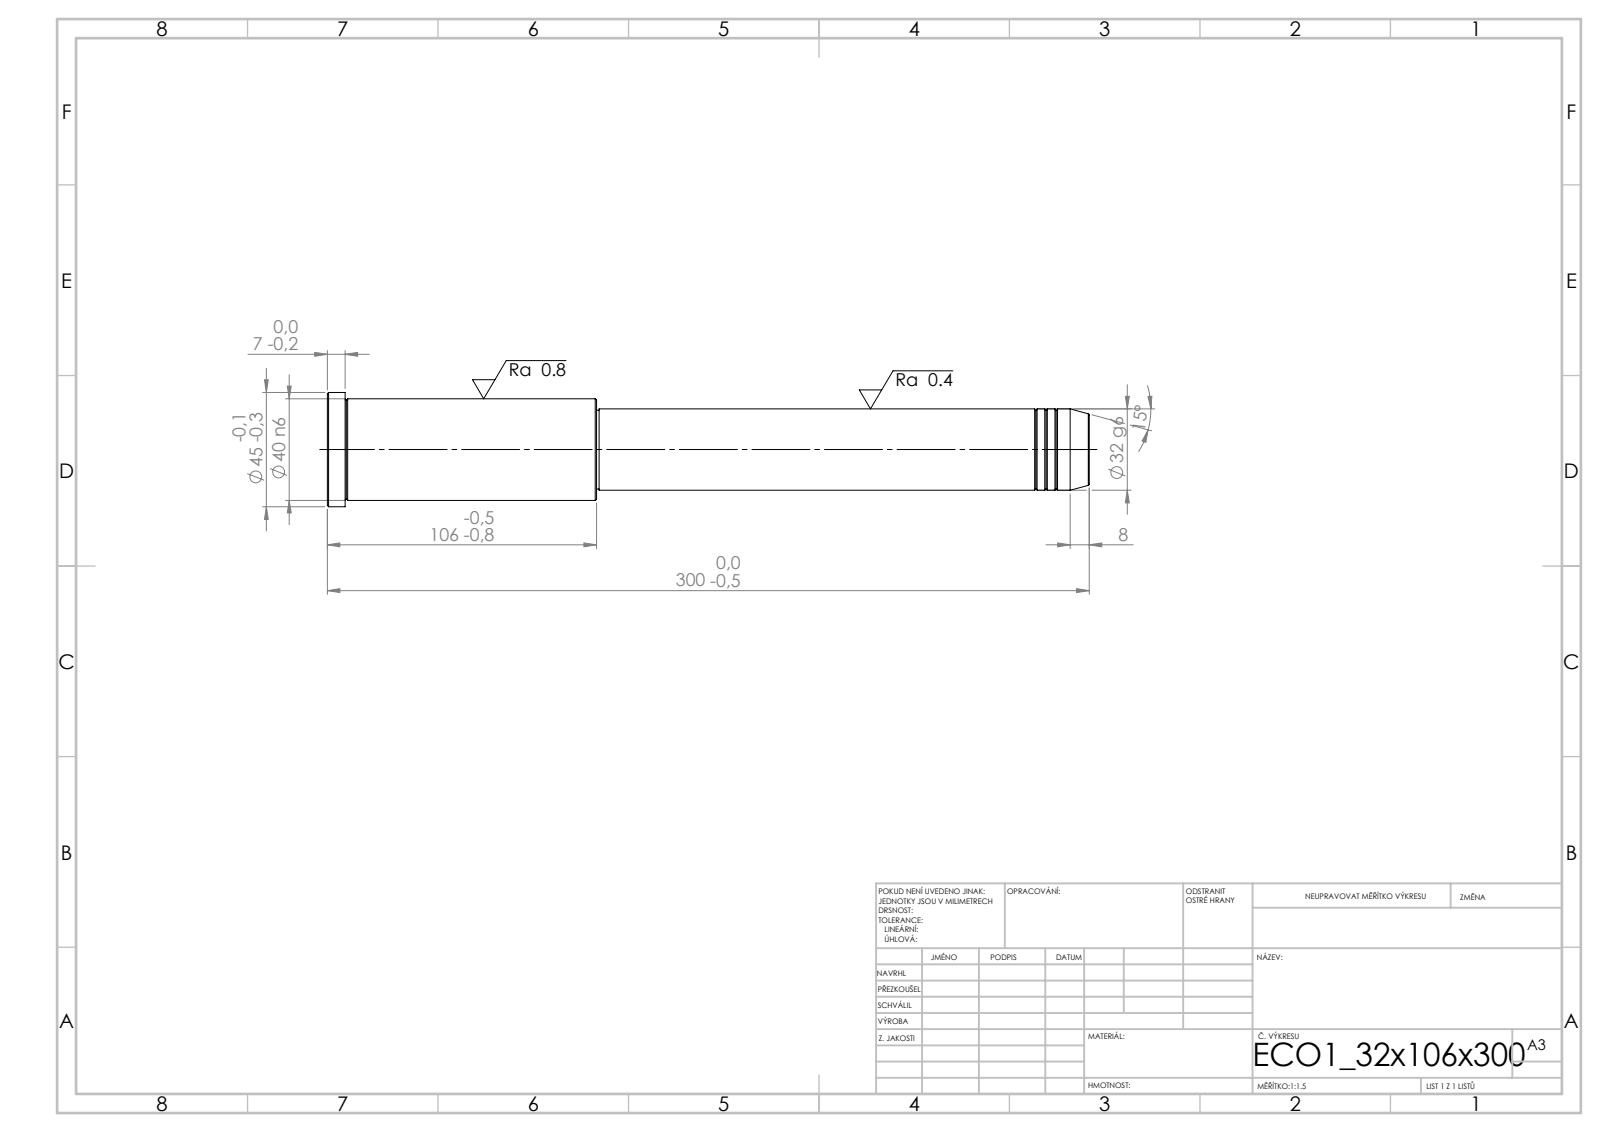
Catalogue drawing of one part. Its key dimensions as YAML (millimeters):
step_written_by: "SolidWorks 2019 (CONFIG_CONTROL_DESIGN)"
units: millimeters
bodies: {solids: 1, faces: 43, planar: 5, cylindrical: 14, other: 24}
overall_size: [300, 45, 45]
volume: 290588
surface_area: 36141
round_bosses_or_shafts:
  - {diameter: 45, count: 1}
  - {diameter: 40, count: 1}
  - {diameter: 32, count: 1}
  - {diameter: 31, count: 1}
face_to_face_distances: [300, 194, 106, 293, 99, 7, 193, 1, 100, 107]
